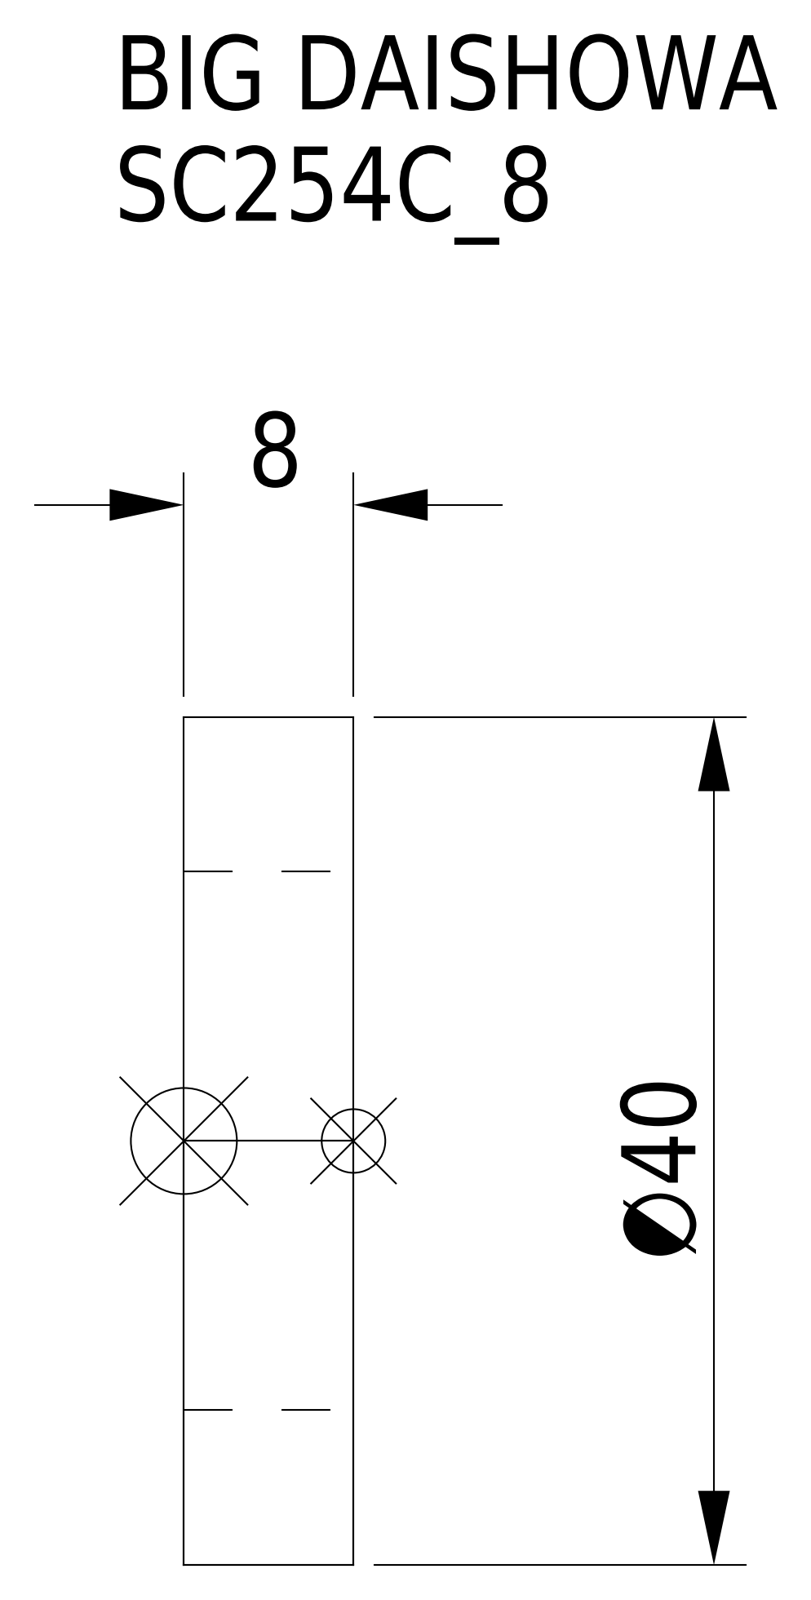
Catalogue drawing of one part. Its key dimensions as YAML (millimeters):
part_name: "SC254C_8"
step_written_by: "CREO PARAMETRIC BY PTC INC, 2016380 (AUTOMOTIVE_DESIGN)"
units: millimeters
bodies: {solids: 1, faces: 8, planar: 5, cylindrical: 3, other: 0}
overall_size: [40, 40, 8]
volume: 5852
surface_area: 3156
round_holes:
  - {diameter: 25.4, count: 1}
round_bosses_or_shafts:
  - {diameter: 40, count: 1}
face_to_face_distances: [8, 6.5]
